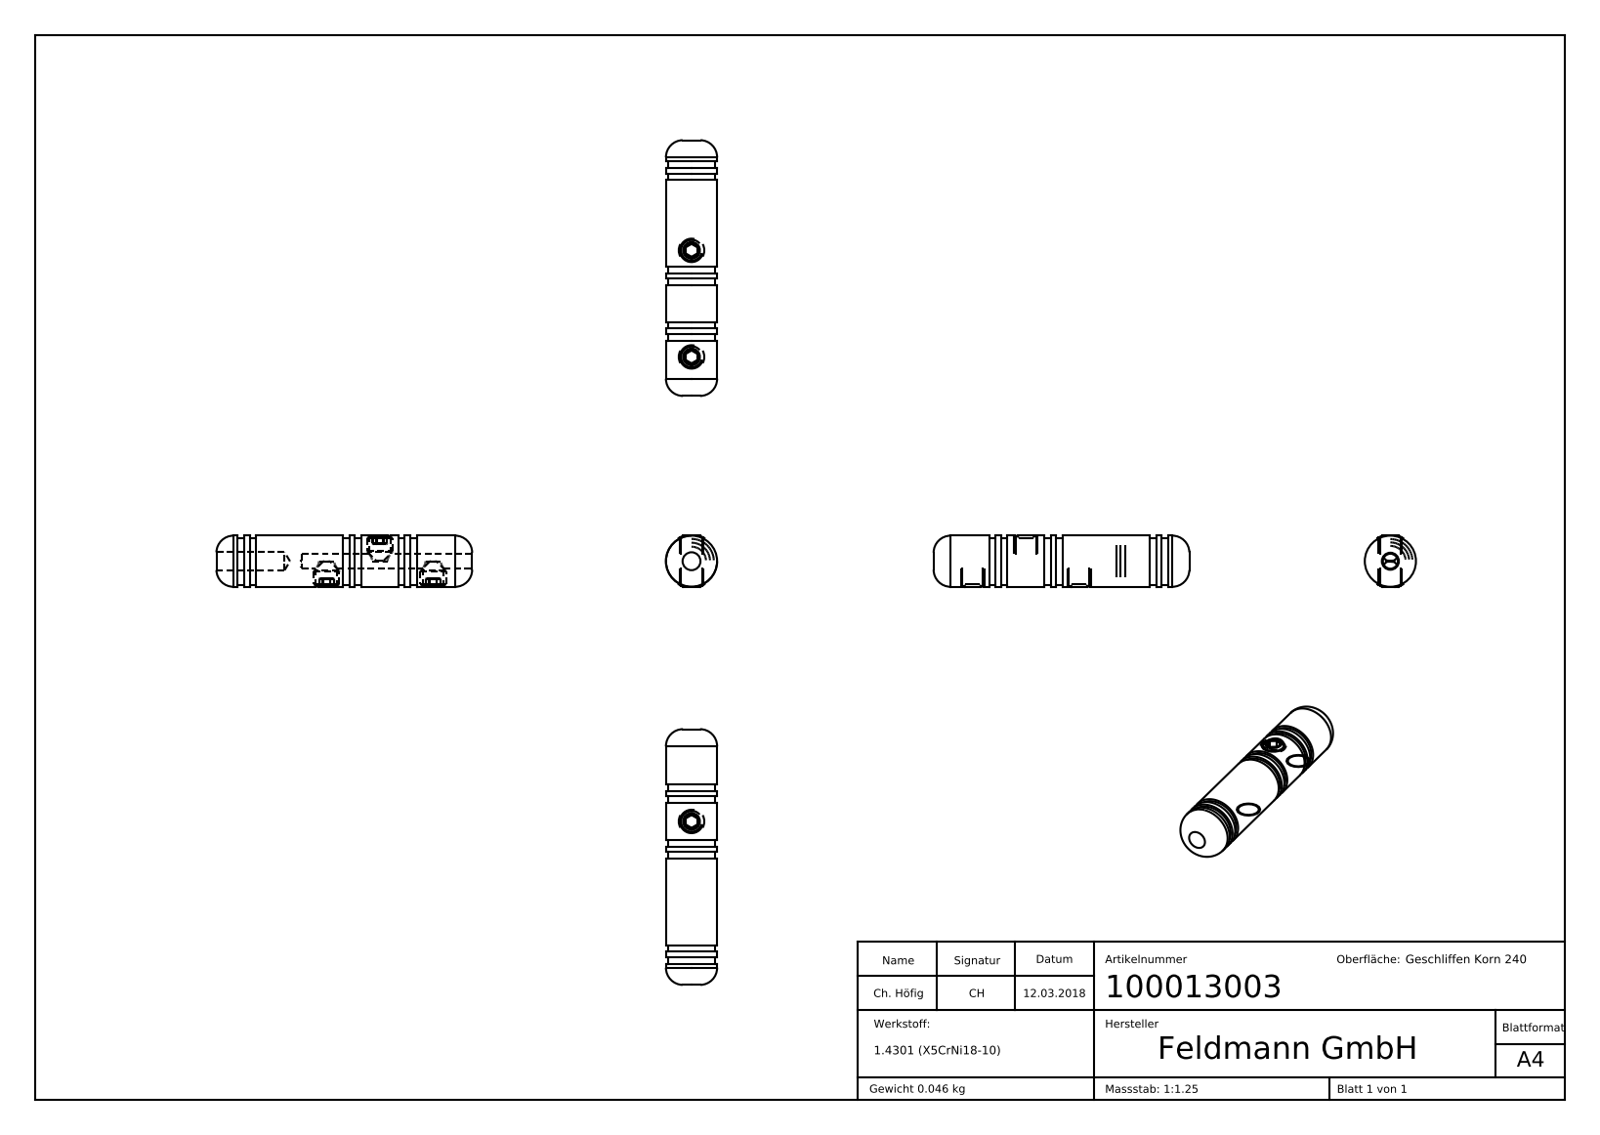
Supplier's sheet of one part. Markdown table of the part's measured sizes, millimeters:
| quantity | value |
| --- | --- |
| part name | DIN914_DIN 914 M6x6; 10001X00X Teil 1_100013003 Teil1; 100013003 |
| STEP written by | SolidWorks 2015 (CONFIG_CONTROL_DESIGN) |
| units | millimeters |
| bodies | 4 solids, 427 faces (144 planar, 96 cylindrical, 187 other) |
| overall size | 60 × 12 × 12 |
| volume | 5 851 mm³ |
| surface area | 3 750 mm² |
| round holes (diameter × count) | 5 × 3, 3.5 × 1, 4.2 × 1 |
| round bosses / shafts (diameter × count) | 6 × 3, 12 × 1, 11 × 1 |
| partial cylindrical surfaces (radius × count) | 0.2 × 50 |
| main face-to-face distances | 1.5, 2.8, 13, 37.7, 24.7, 1.3, 4.3, 15.8, 27.5, 14.5 |
| hole center spacings | 12.5, 25 |
